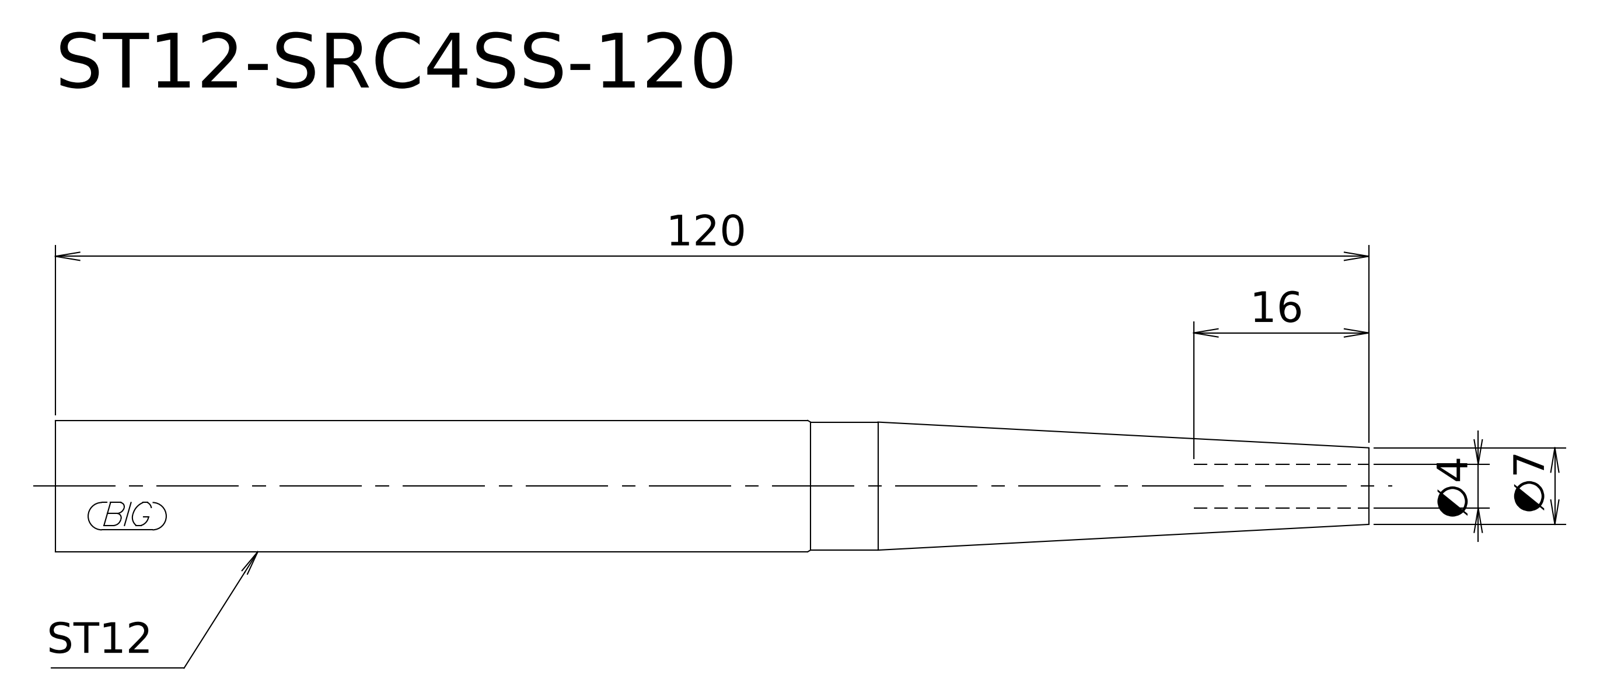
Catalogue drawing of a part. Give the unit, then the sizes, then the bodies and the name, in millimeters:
Units: millimetres
Overall size (bounding box): 120 × 12 × 12
Round bosses / shafts (diameter × count): ⌀12 ×1, ⌀11.7 ×1
Main face-to-face distances: 120
Volume: 11 609 mm³ · Surface area: 4 300 mm²
Bodies: 1 solid, 6 faces (2 planar, 2 cylindrical, 2 other)
STEP written by: Kubotek KeyCreator V8.5.1 (14335) (CONFIG_CONTROL_DESIGN)
